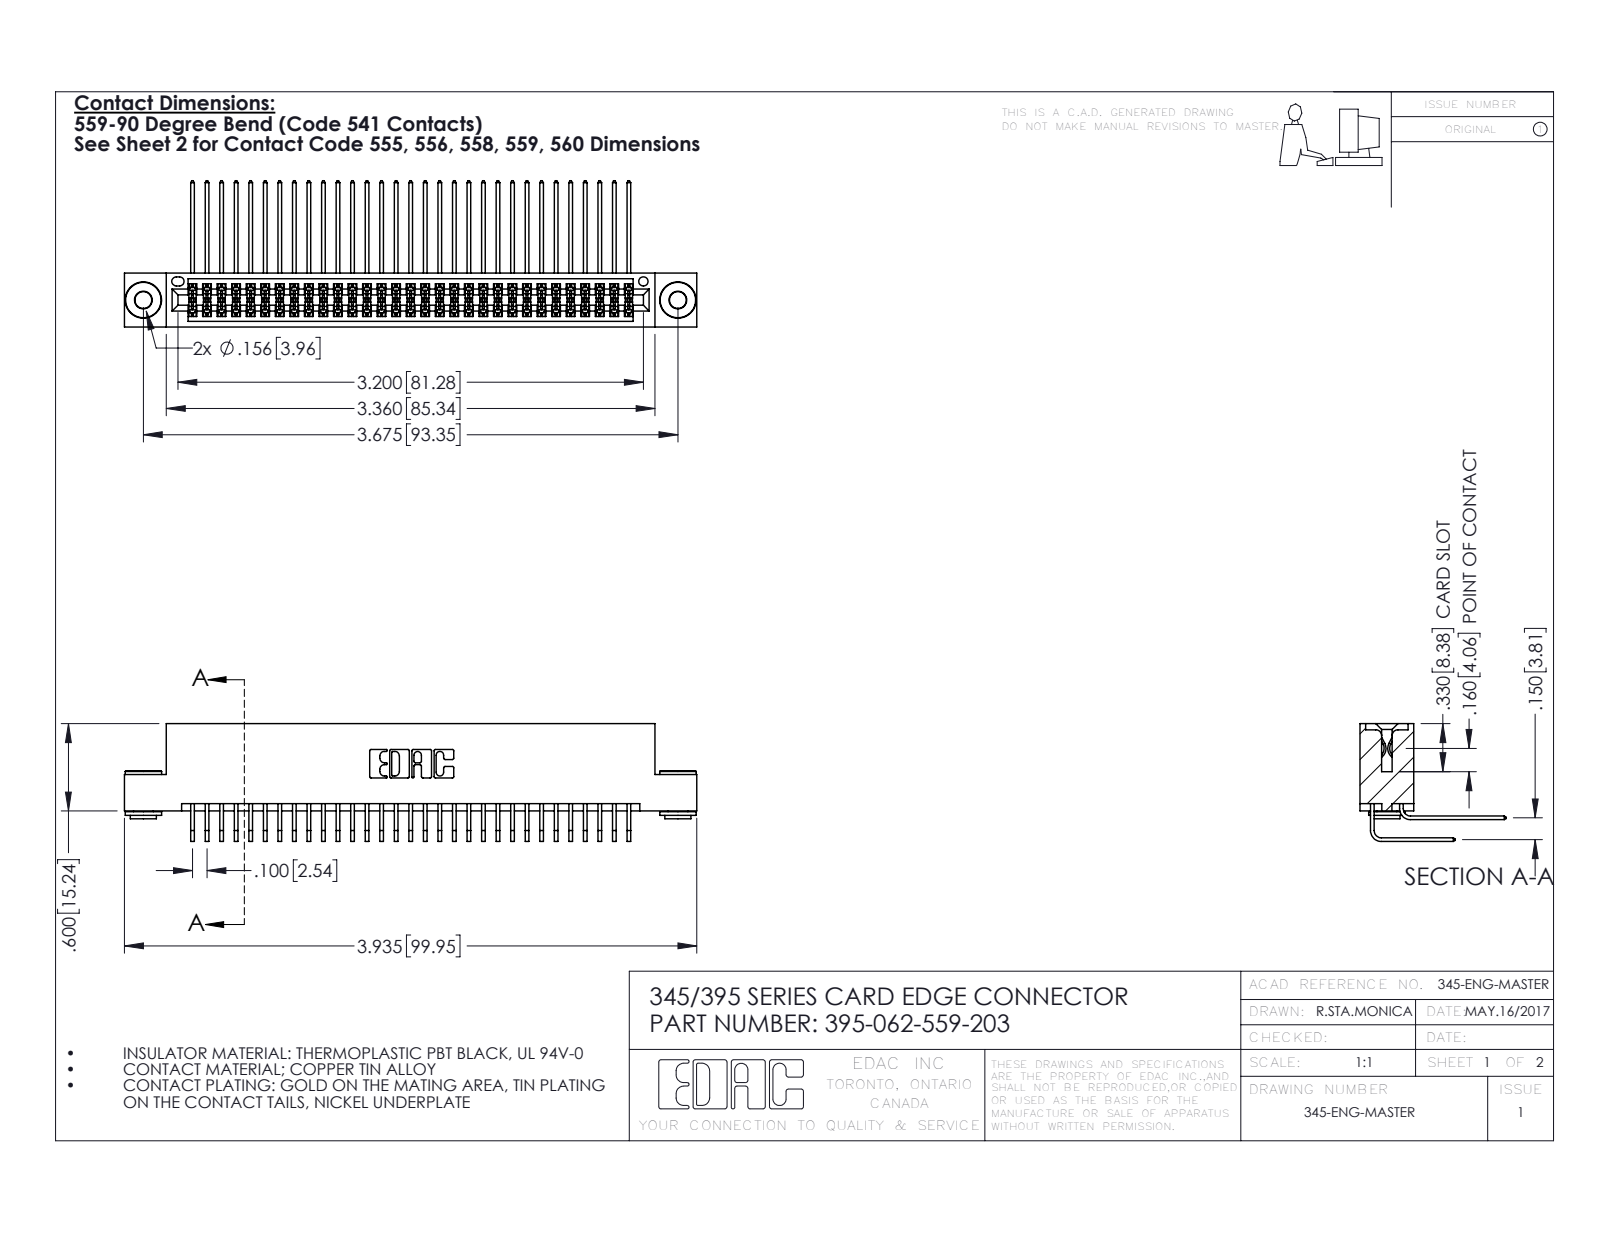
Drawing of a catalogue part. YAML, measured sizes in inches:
part_name: "345-292-001_558 559 Tail - 1; 345-250-002_345-250-002-102; 395-062-559-203; 345 Part_Flush Mounting Lugs - 0.156 Dia-TH (+1 more)"
step_written_by: "SolidWorks 2016 (CONFIG_CONTROL_DESIGN)"
units: inches
bodies: {solids: 65, faces: 3388, planar: 2260, cylindrical: 1120, other: 8}
overall_size: [3.935, 1.005, 0.809]
volume: 0.609
surface_area: 25.47
round_holes:
  - {diameter: 0.116, count: 2}
  - {diameter: 0.156, count: 2}
  - {diameter: 0.064, count: 1}
round_bosses_or_shafts:
  - {diameter: 0.25, count: 2}
  - {diameter: 0.18, count: 2}
  - {diameter: 0.136, count: 2}
partial_cylinders:
  - {radius: 0.006, count: 94}
  - {radius: 0.01, count: 22}
  - {radius: 0.007, count: 6}
  - {radius: 0.031, count: 6}
  - {radius: 0.026, count: 3}
  - {radius: 0.014, count: 2}
  - {radius: 0.019, count: 2}
  - {radius: 0.022, count: 2}
face_to_face_distances: [0.072, 0.298, 0.2, 0.37, 0.025, 0.098, 0.272, 0.225, 0.15, 0.175]
hole_center_spacings: [0.27, 3.44, 3.675]
